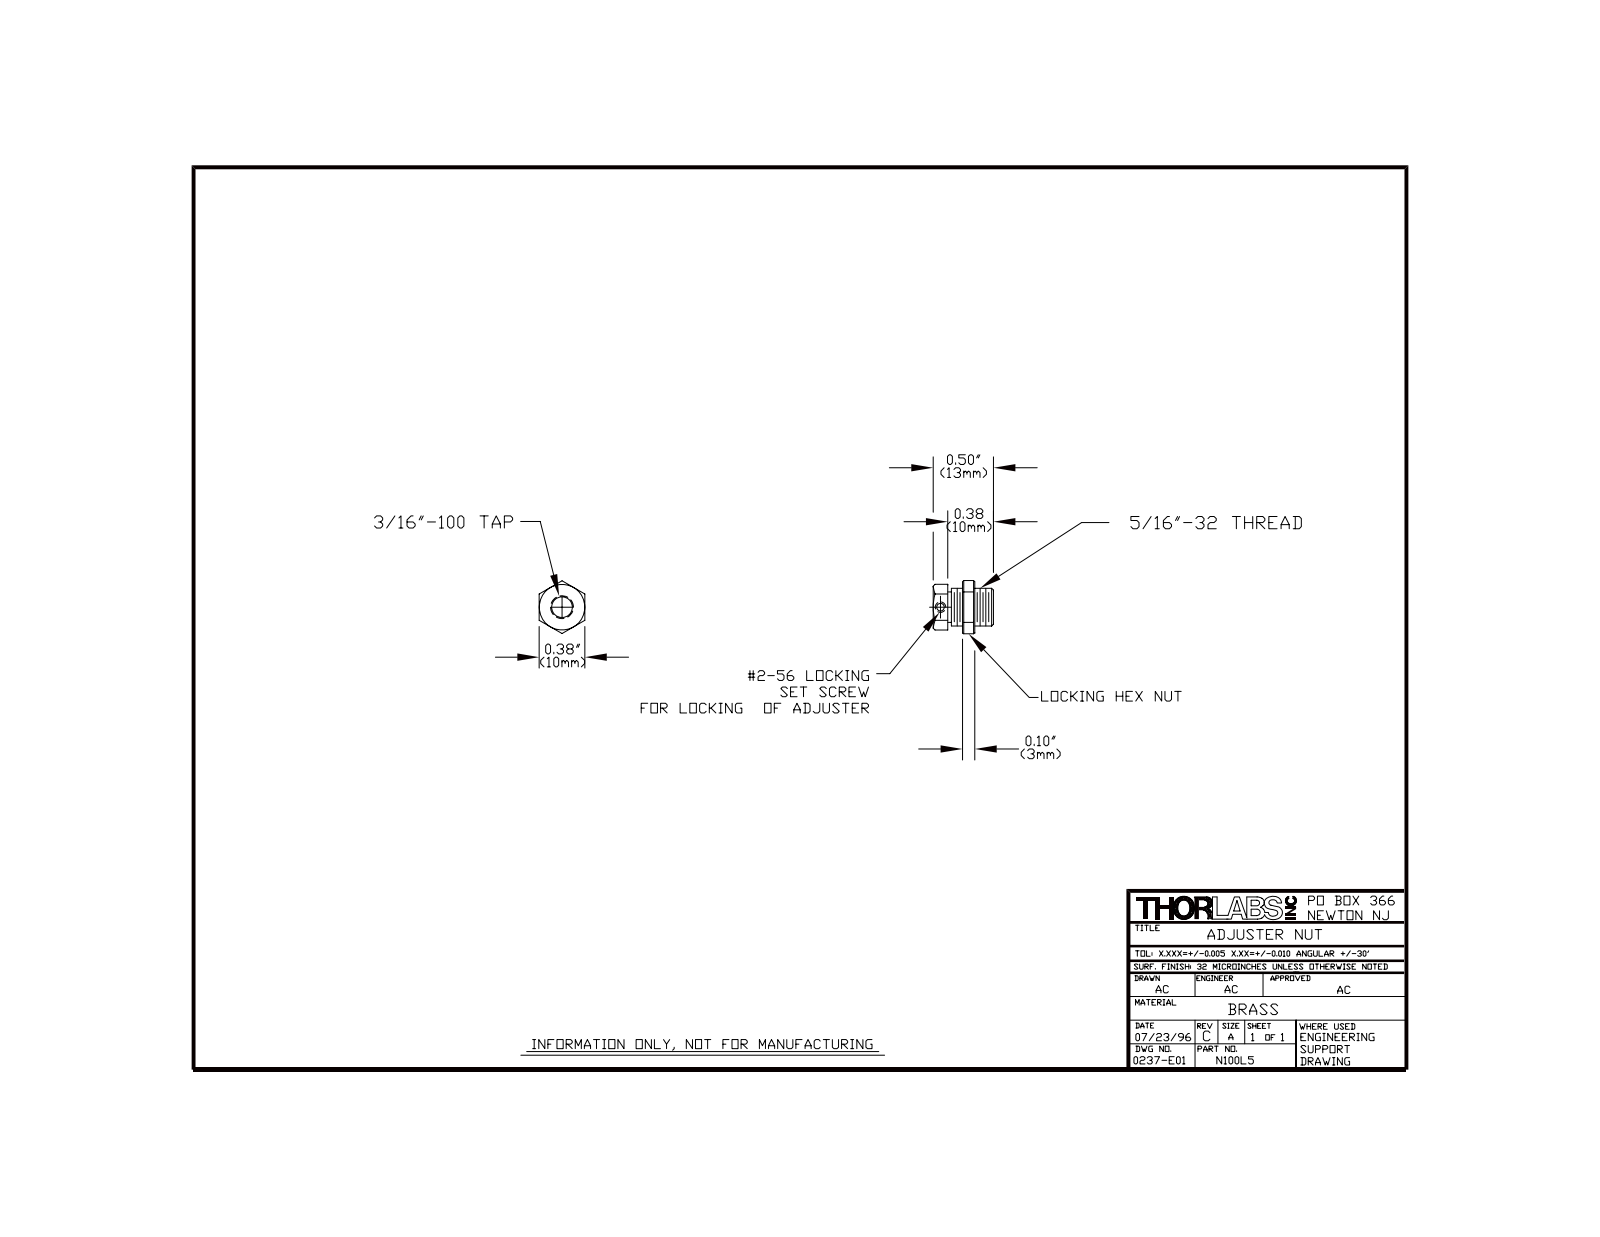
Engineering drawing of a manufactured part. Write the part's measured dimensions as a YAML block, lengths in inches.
part_name: "0237-E0W"
step_written_by: "SolidWorks 2007 (AUTOMOTIVE_DESIGN)"
units: inches
bodies: {solids: 2, faces: 39, planar: 19, cylindrical: 12, other: 8}
overall_size: [0.5, 0.433, 0.375]
volume: 0.031
surface_area: 1.086
round_holes:
  - {diameter: 0.086, count: 1}
  - {diameter: 0.17, count: 1}
round_bosses_or_shafts:
  - {diameter: 0.307, count: 1}
  - {diameter: 0.25, count: 1}
  - {diameter: 0.057, count: 1}
face_to_face_distances: [0.125, 0.375, 0.375, 0.5, 0.345, 0.03, 0.155, 0.25, 0.035, 0.035]
